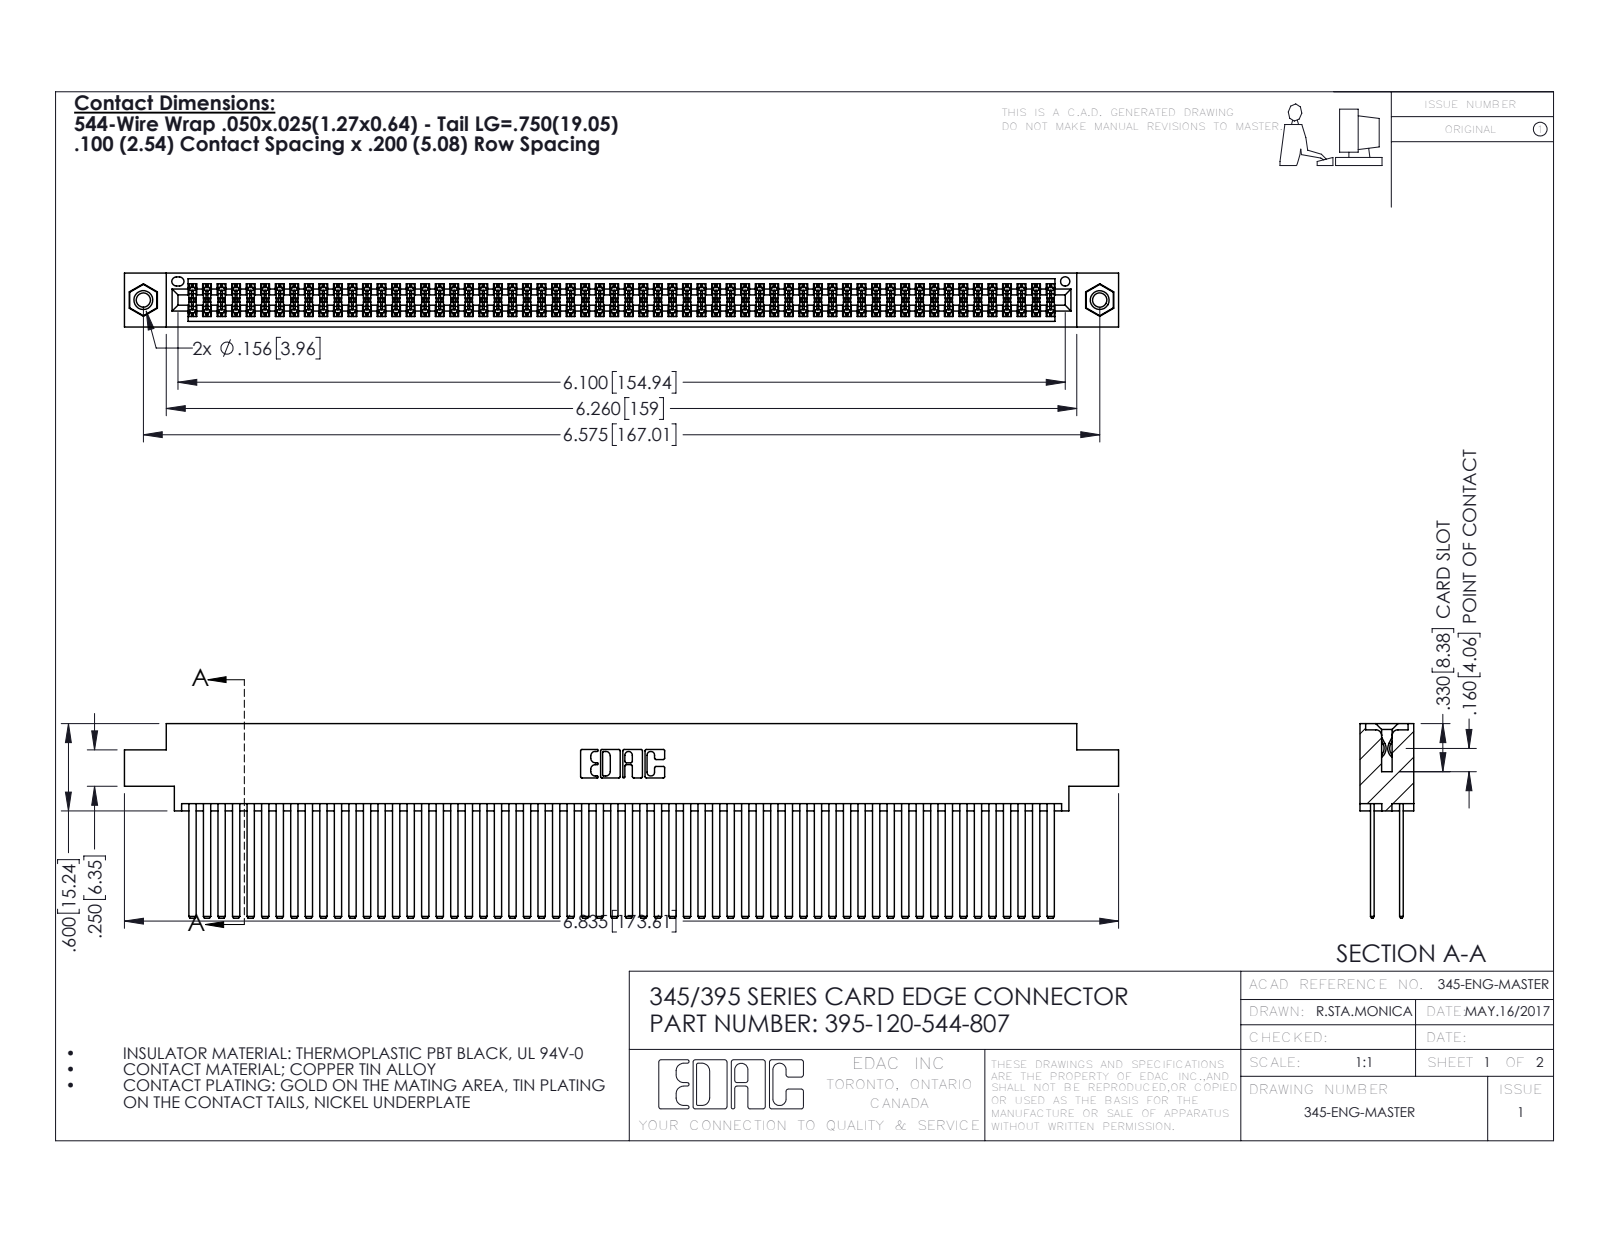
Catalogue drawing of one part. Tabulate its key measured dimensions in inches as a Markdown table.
| quantity | value |
| --- | --- |
| part name | 345-292-001_345-293-144; 395-120-544-807; 345 Part_0.170 Offset - 0.156 Dia-TI; 345-250-001_345-250-005-103 |
| STEP written by | SolidWorks 2016 (CONFIG_CONTROL_DESIGN) |
| units | inches |
| bodies | 123 solids, 5470 faces (3596 planar, 1858 cylindrical, 16 other) |
| overall size | 6.835 × 1.337 × 0.37 |
| volume | 1.134 in³ |
| surface area | 51.03 in² |
| round holes (diameter × count) | 0.098 × 2, 0.125 × 2, 0.156 × 2, 0.064 × 1 |
| round bosses / shafts (diameter × count) | 0.155 × 2 |
| partial cylindrical surfaces (radius × count) | 0.006 × 180, 0.01 × 22, 0.007 × 6, 0.031 × 6, 0.026 × 3, 0.014 × 2, 0.019 × 2, 0.022 × 2 |
| main face-to-face distances | 0.2, 0.025, 0.072, 0.098, 0.272, 0.298, 0.225, 0.175, 0.37, 0.15 |
| hole center spacings | 0.27, 6.339, 6.575 |
